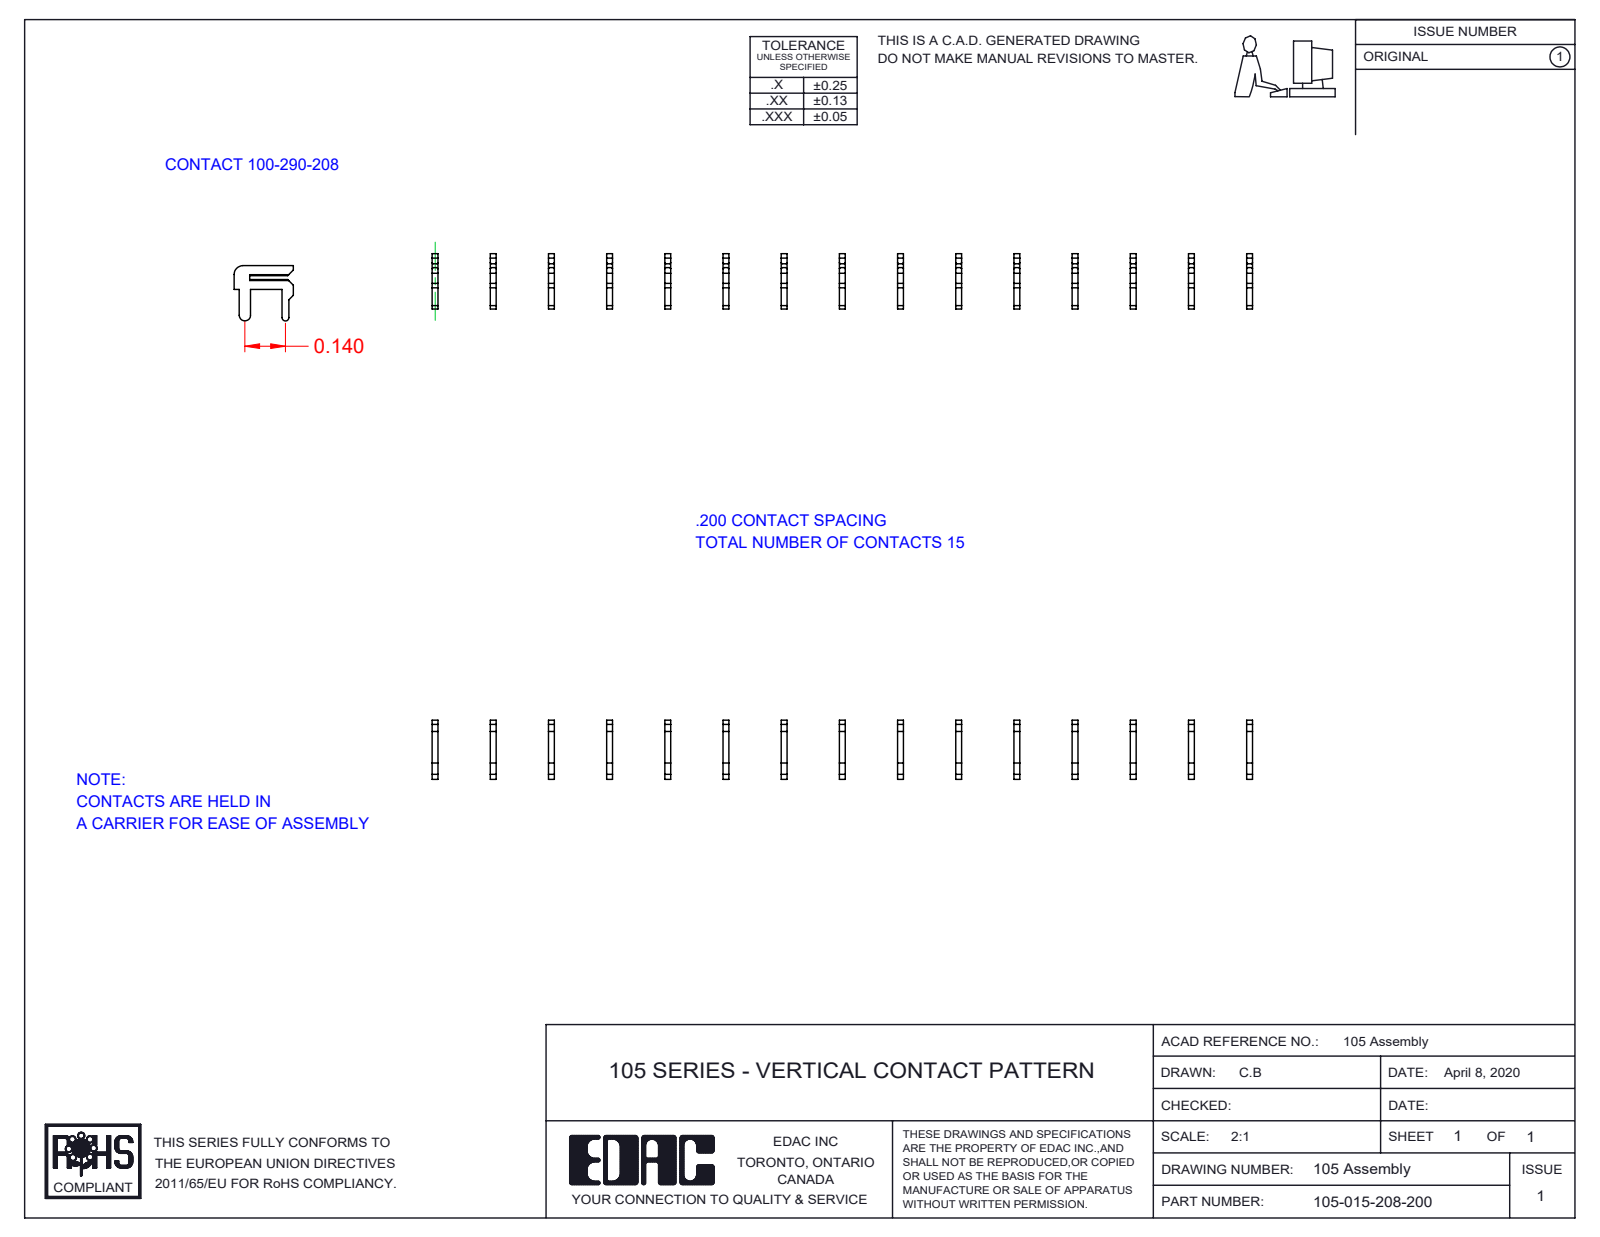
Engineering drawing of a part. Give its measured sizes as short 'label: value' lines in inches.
name: 100-290-001_100-290-208; 105-015-208-200
written by: SolidWorks 2016 (CONFIG_CONTROL_DESIGN)
unit: in
bodies: 15 solids, 375 faces (330 planar, 45 cylindrical, 0 other)
size: 2.82 × 0.204 × 0.19
volume: 0.006 in³; area: 0.988 in²
rounds: 1× R0.012, 1× R0.019, 1× R0.03
face distances: 0.2, 0.4, 0.6, 0.8, 1, 1.2, 1.4, 1.6, 1.8, 2
